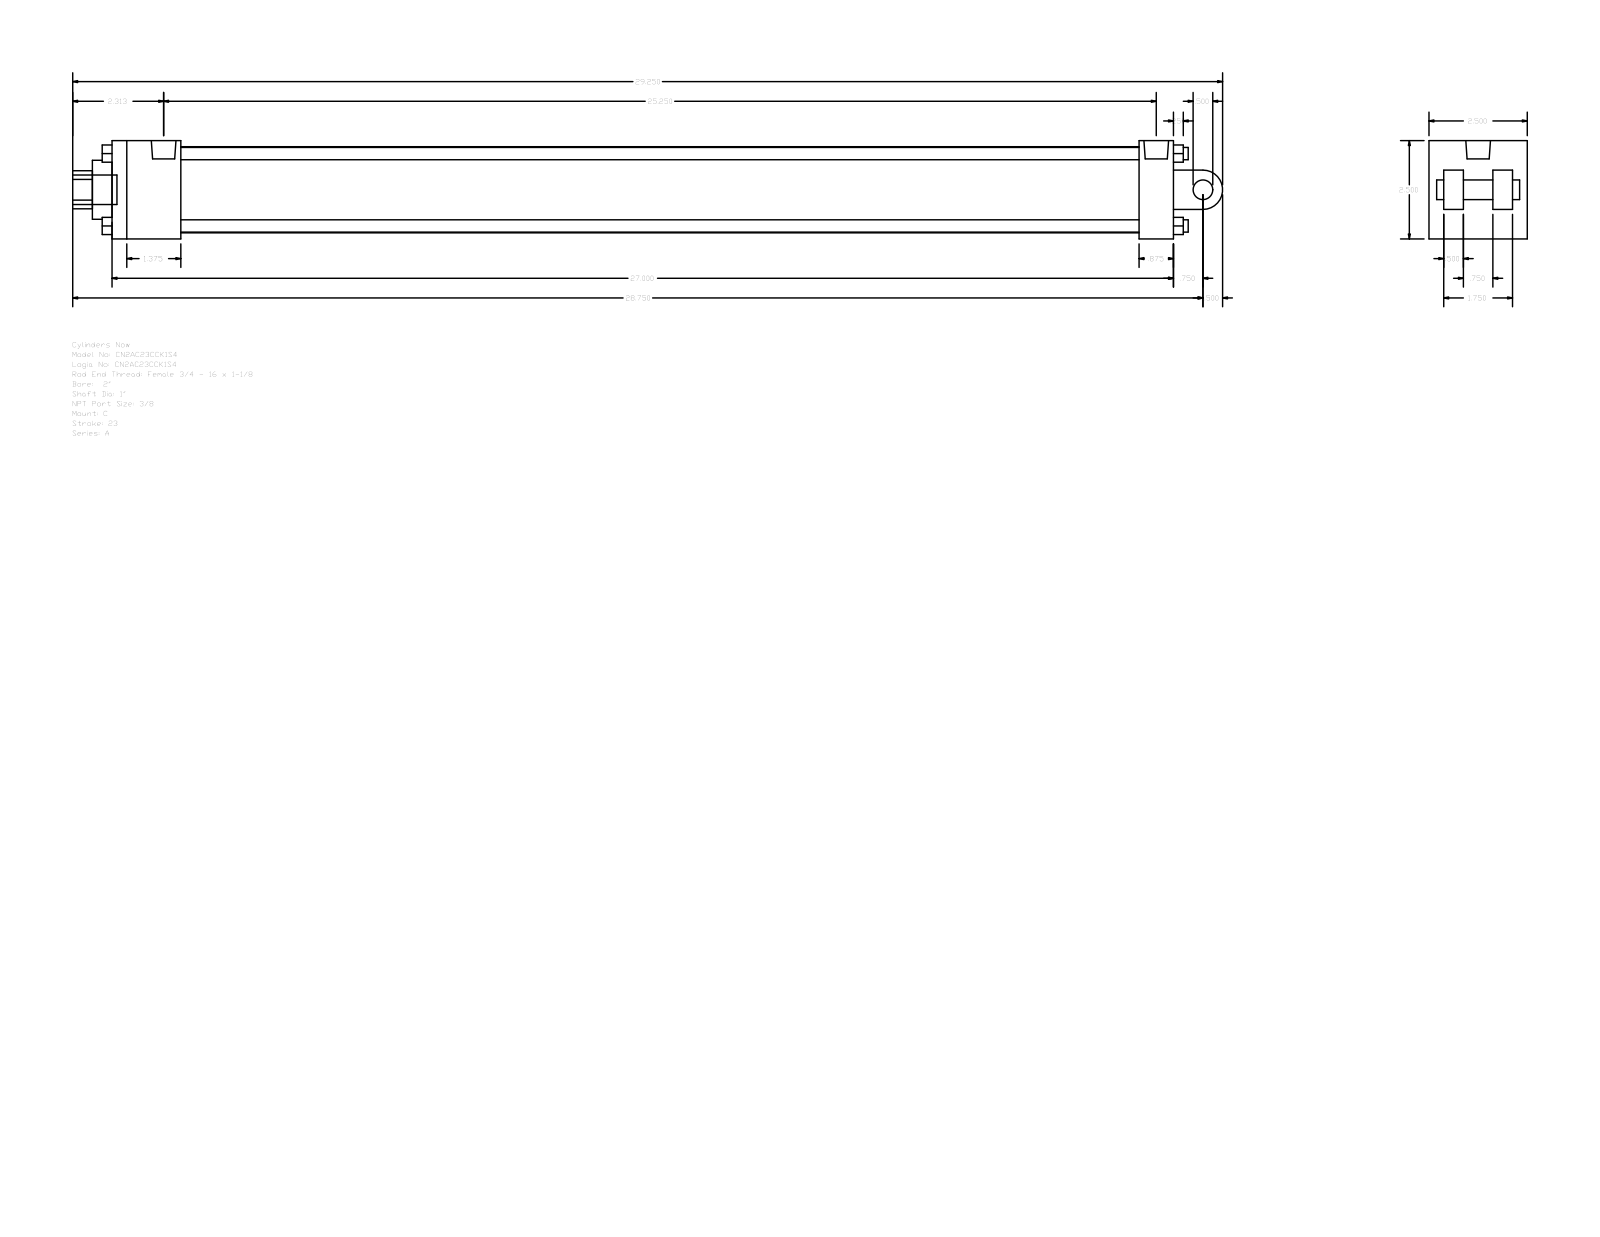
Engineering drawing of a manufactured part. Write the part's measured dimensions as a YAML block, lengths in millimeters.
part_name: "A_C__0200_1"
step_written_by: "GSSL Pune (CONFIG_CONTROL_DESIGN)"
units: millimeters
bodies: {solids: 0, faces: 135, planar: 102, cylindrical: 33, other: 0}
overall_size: [742.95, 63.5, 63.5]
round_holes:
  - {diameter: 5.56, count: 2}
  - {diameter: 15.93, count: 1}
  - {diameter: 25.4, count: 1}
  - {diameter: 38.1, count: 1}
  - {diameter: 55.63, count: 1}
round_bosses_or_shafts:
  - {diameter: 7.94, count: 4}
  - {diameter: 5.56, count: 2}
  - {diameter: 19.05, count: 1}
  - {diameter: 15.93, count: 1}
  - {diameter: 12.7, count: 1}
partial_cylinders:
  - {radius: 12.29, count: 1}
  - {radius: 12.7, count: 1}
face_to_face_distances: [63.5, 22.22, 685.8, 44.45, 12.7, 9.52, 41.28, 641.35, 663.58, 619.13]
hole_center_spacings: [3.98]
